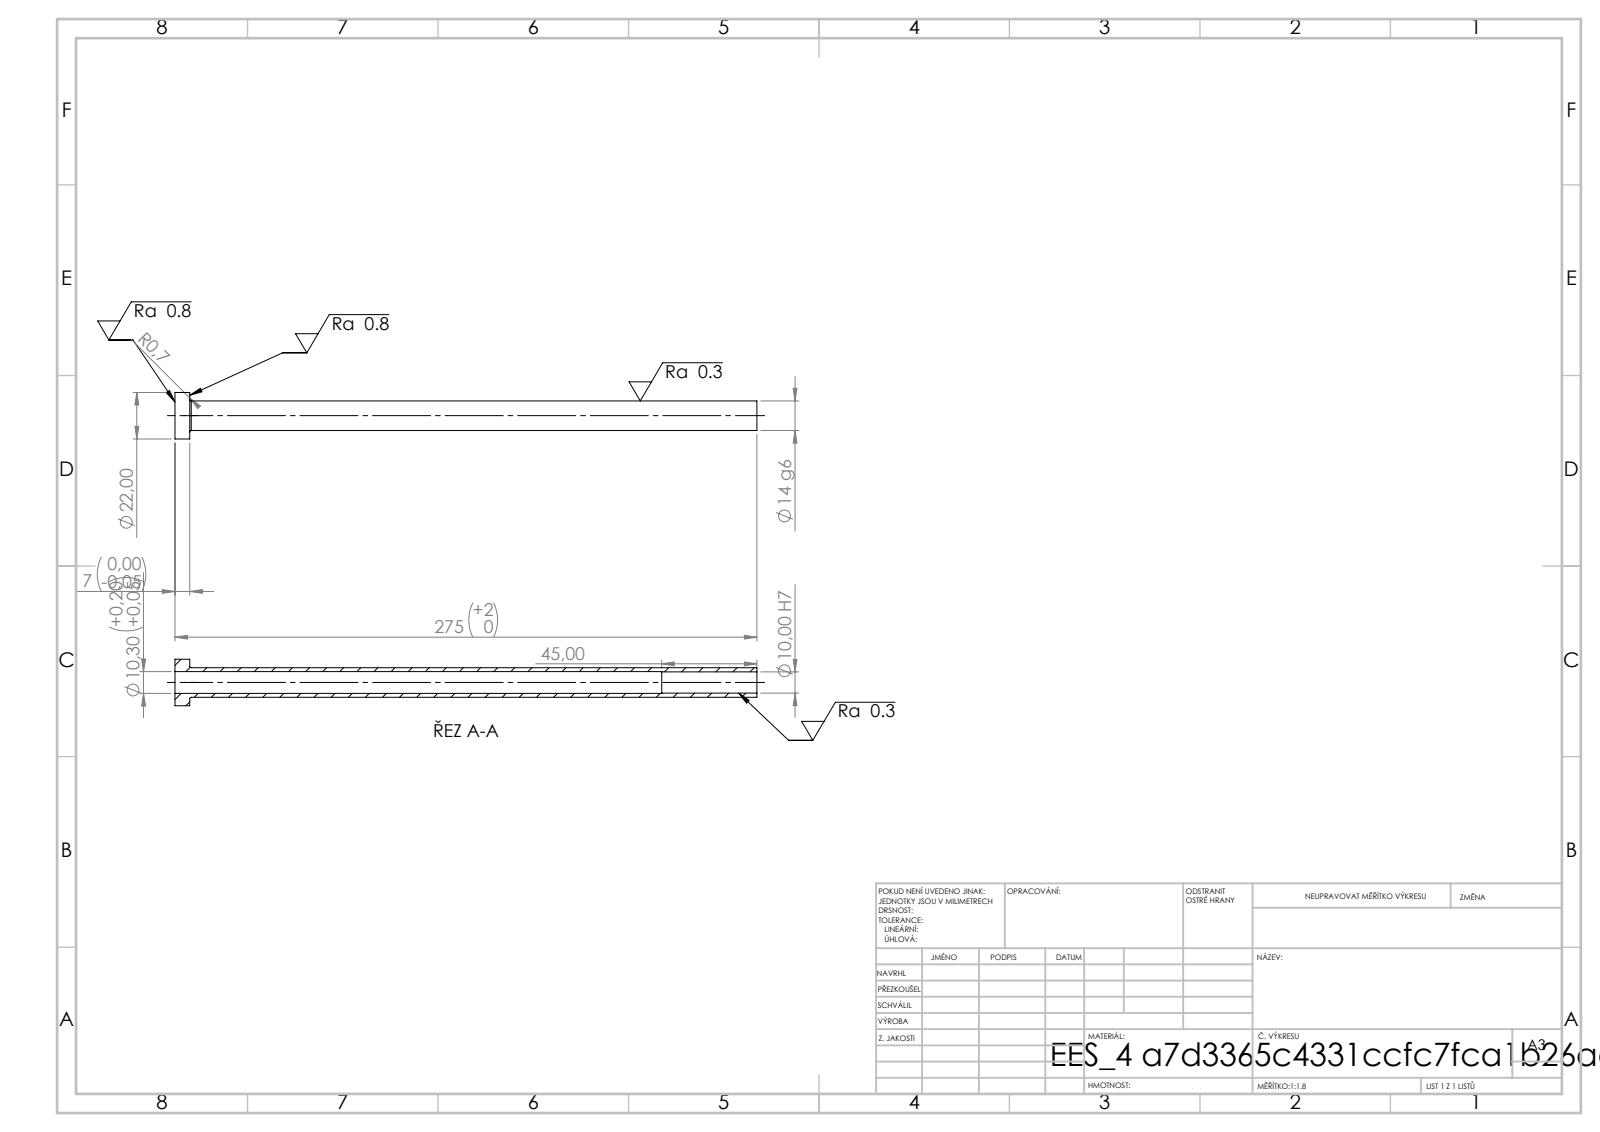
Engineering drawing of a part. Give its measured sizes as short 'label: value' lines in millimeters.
written by: SolidWorks 2019 (CONFIG_CONTROL_DESIGN)
unit: mm
bodies: 1 solid, 14 faces (4 planar, 8 cylindrical, 2 other)
size: 275 × 22 × 22
volume: 21 222 mm³; area: 21 717 mm²
holes: 1× ⌀10, 1× ⌀10.3
bosses: 1× ⌀22, 1× ⌀14
face distances: 7, 275, 268, 230, 223, 45
